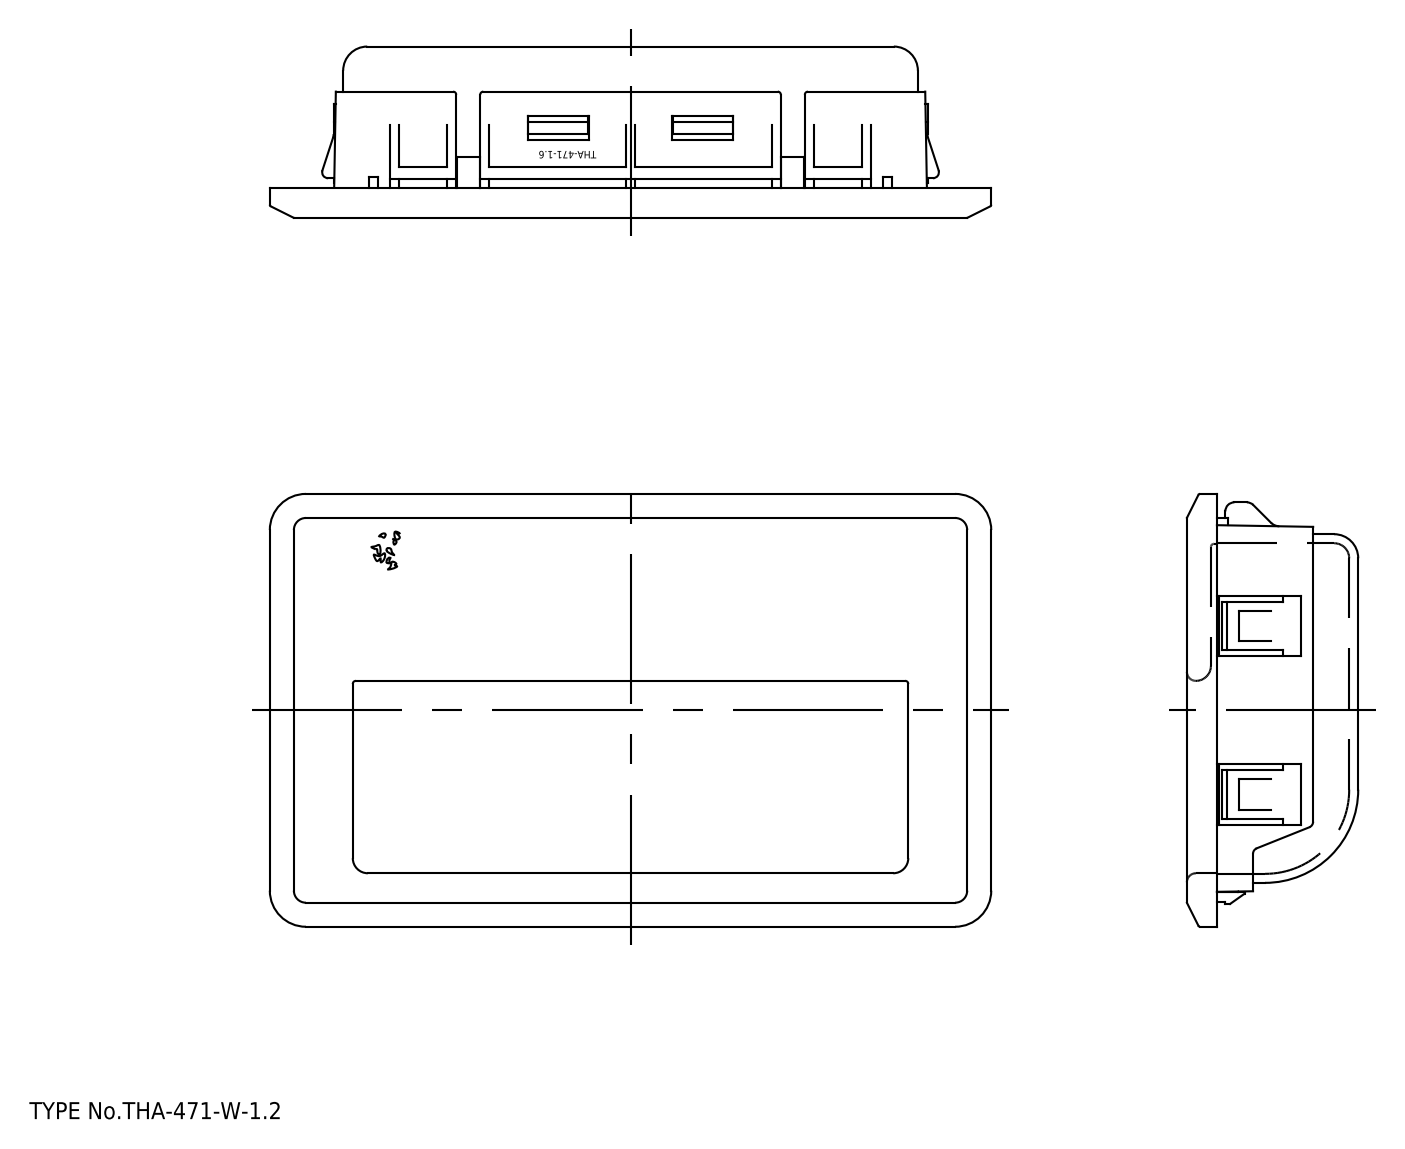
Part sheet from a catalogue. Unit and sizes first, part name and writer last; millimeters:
Units: millimetres
Overall size (bounding box): 120 × 72 × 28.5
Partial cylindrical surfaces — rounded edges, fillets, slot ends (radius × count): R0.5 ×137, R4 ×17, R2.5 ×10, R0.3 ×8, R2 ×7, R1.5 ×6, R1 ×4, R3 ×4
Main face-to-face distances: 1.5, 28.5, 27, 5, 22, 23.5, 2, 94.1, 3, 56.5
Volume: 41 621 mm³ · Surface area: 45 703 mm²
Bodies: 1 solid, 975 faces (428 planar, 355 cylindrical, 192 other)
STEP written by: spGate 16.7.1 (AUTOMOTIVE_DESIGN)
